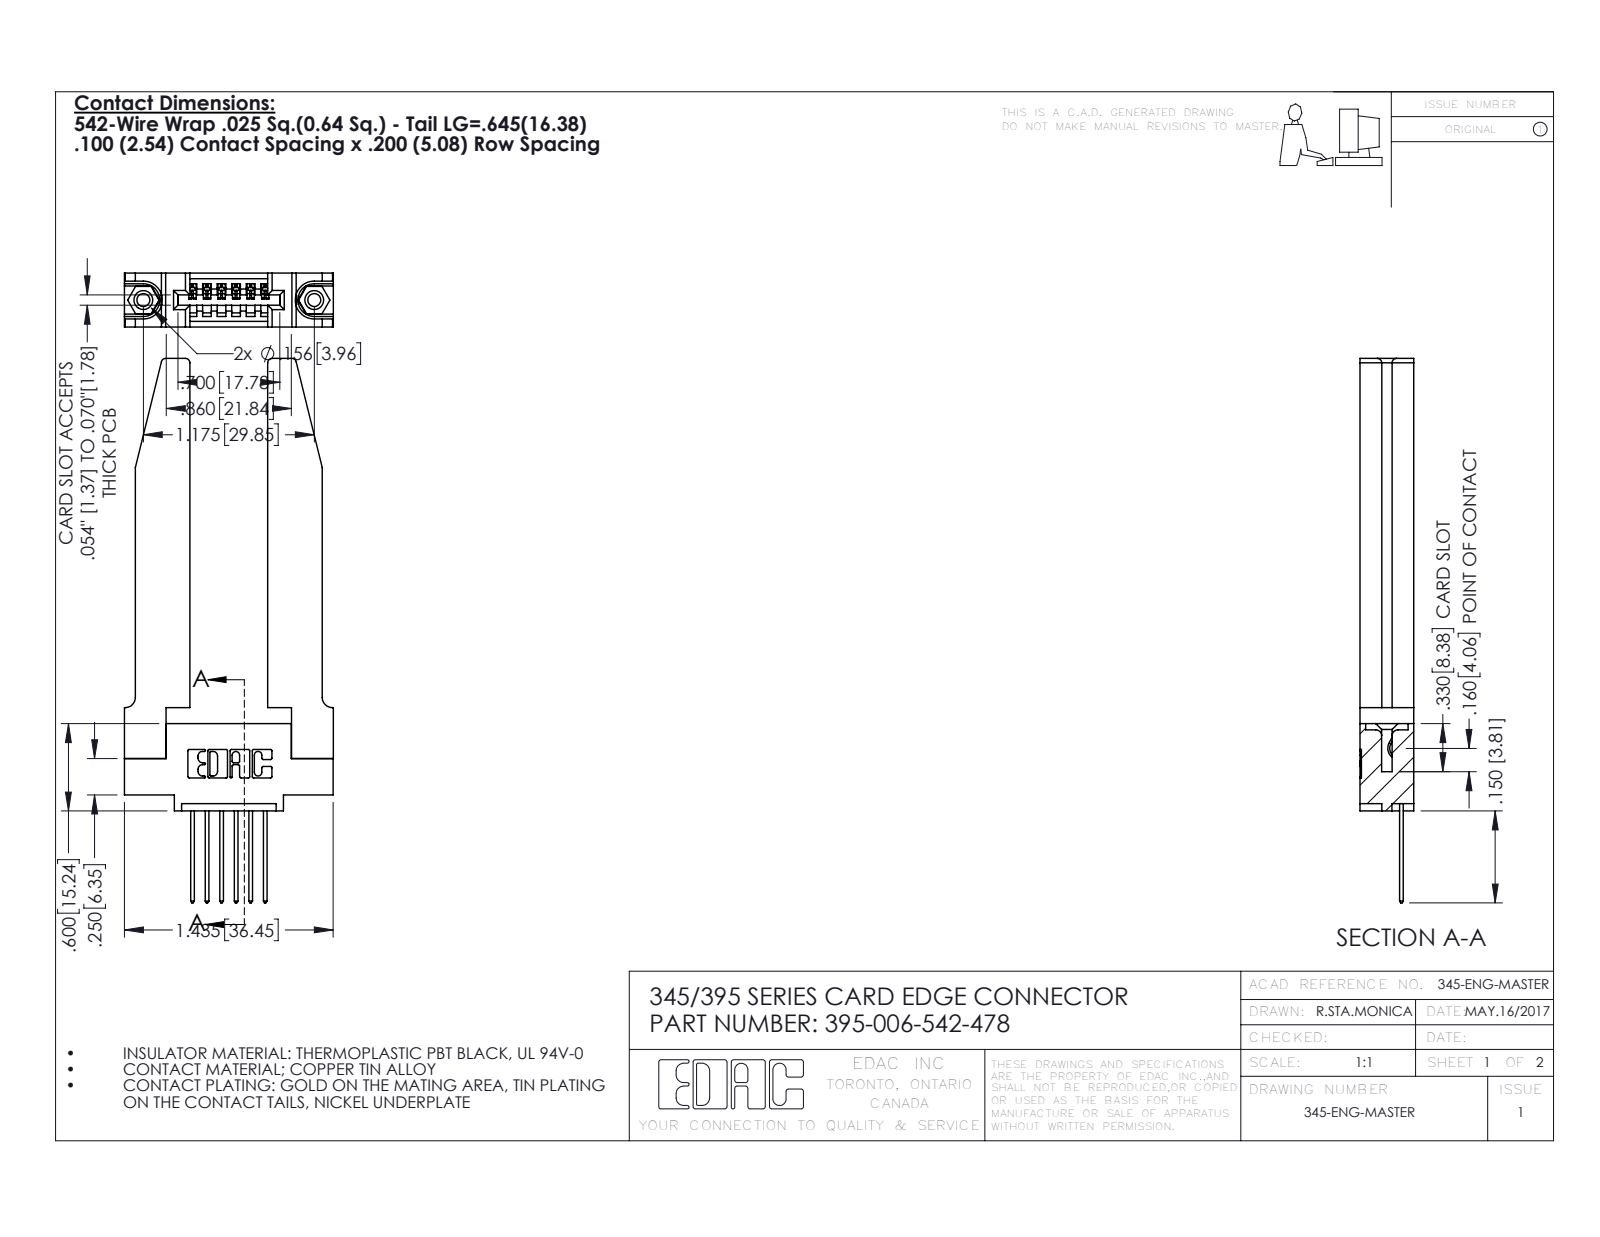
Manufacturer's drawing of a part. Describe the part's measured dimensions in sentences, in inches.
The part is named "345-292-001_345-293-142; 345-220-078_345-220-078; 345-250-001_345-250-001-102; 345 Part_0.110 Offset - 0.156 Dia-TH (+1 more)". Its 3-D file was written by "SolidWorks 2016 (CONFIG_CONTROL_DESIGN)". It is 11 solids with 712 faces: 466 planar, 194 cylindrical and 52 other. Overall it measures 3.742 by 1.436 by 0.37 inches. Its volume is 0.664 cubic inches and its surface area 16.51 square inches. Round holes: 2 of diameter 0.089, 2 of diameter 0.125, 2 of diameter 0.156, 1 of diameter 0.064. Round bosses or shafts: 2 of diameter 0.155. Partial cylindrical surfaces (rounded edges, fillets, slot ends): 22 of radius 0.01, 12 of radius 0.006, 12 of radius 0.01, 8 of radius 0.03, 6 of radius 0.007, 6 of radius 0.031, 3 of radius 0.026, 2 of radius 0.031. The main face-to-face distances are 0.37, 0.15, 0.22, 0.072, 0.535, 0.148, 0.298, 0.077, 0.2, 0.071. The hole center spacings are 0.27, 0.946, 1.175.
